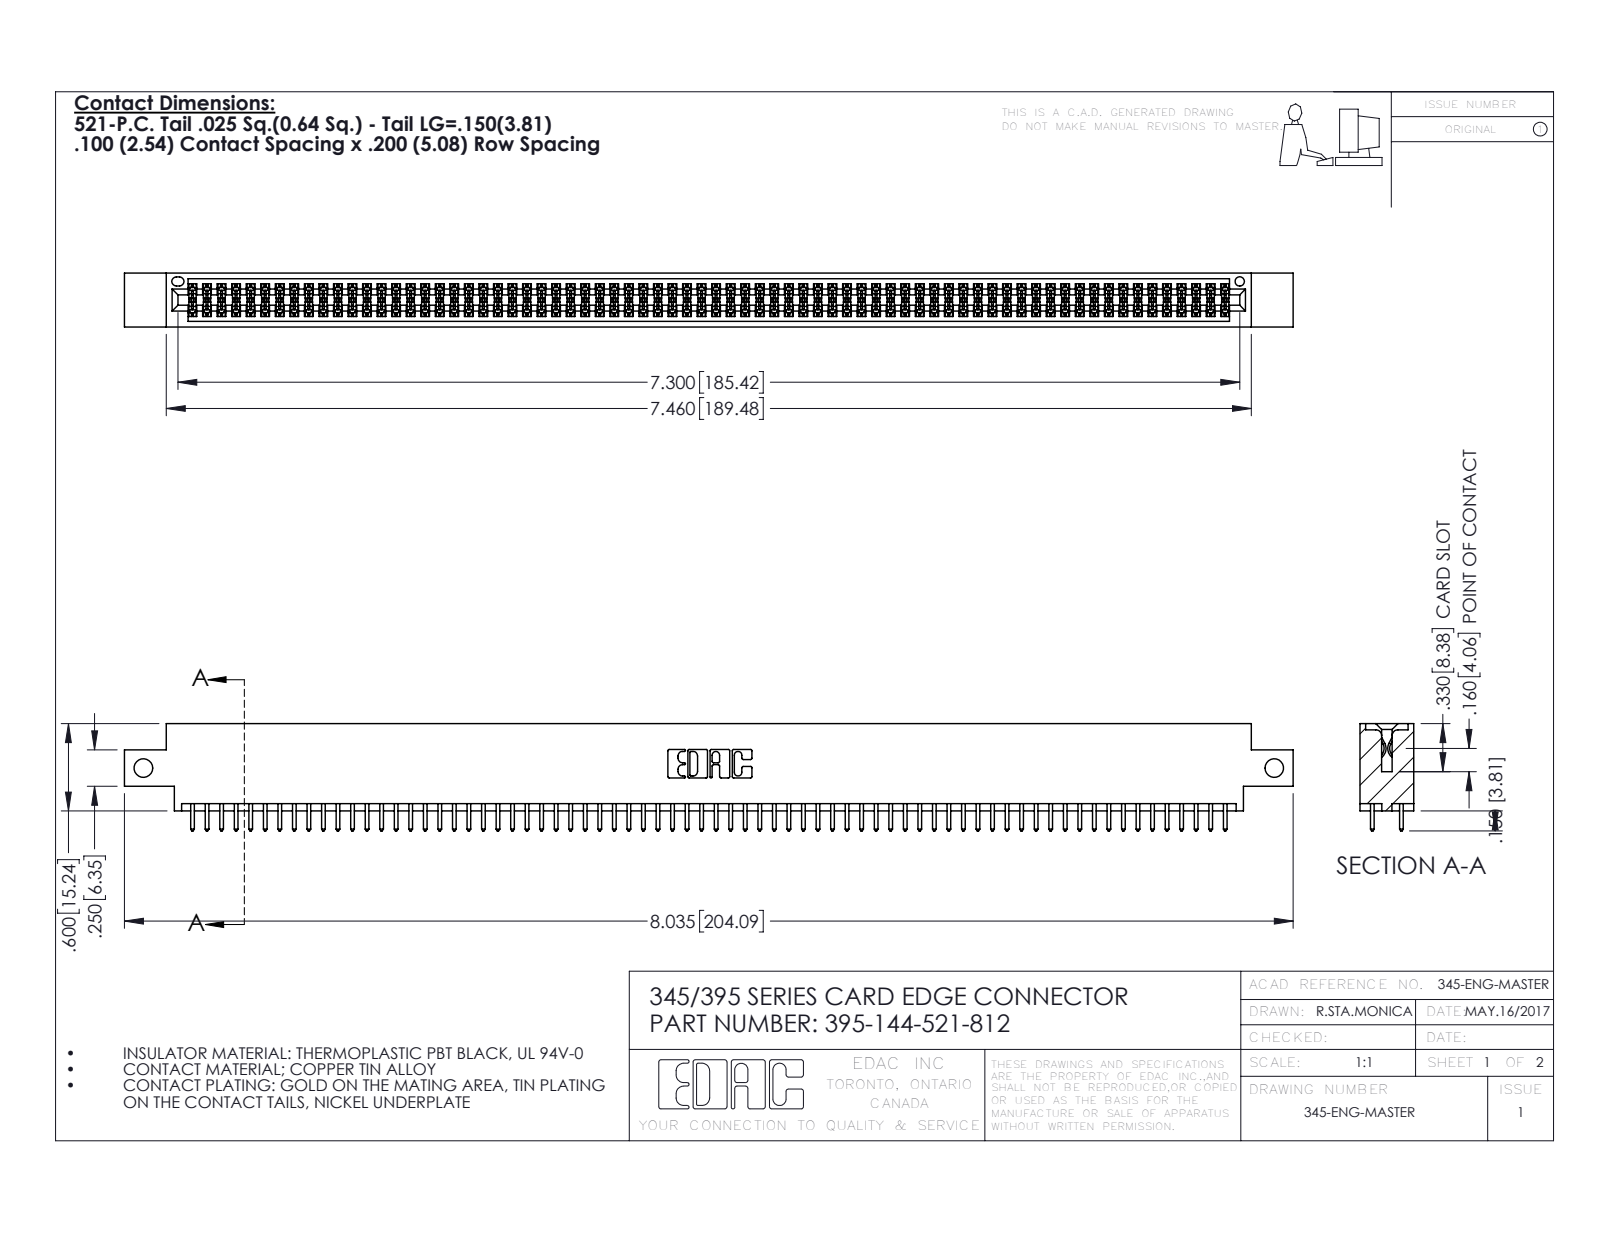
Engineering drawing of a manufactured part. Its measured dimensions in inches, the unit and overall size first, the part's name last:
Units: inches
Overall size (bounding box): 8.035 × 0.737 × 0.37
Round holes (diameter × count): ⌀0.128 ×2, ⌀0.064 ×1
Partial cylindrical surfaces — rounded edges, fillets, slot ends (radius × count): R0.006 ×216, R0.01 ×144, R0.01 ×22, R0.007 ×6, R0.031 ×6, R0.026 ×3, R0.014 ×2, R0.019 ×2
Main face-to-face distances: 0.072, 0.298, 0.2, 0.37, 0.098, 0.272, 0.025, 0.225, 0.175, 0.149
Hole centre spacings: 7.775
Volume: 1.211 in³ · Surface area: 45.79 in²
Bodies: 145 solids, 7330 faces (4836 planar, 2494 cylindrical, 0 other)
Part name (STEP PRODUCT): 345-292-001_345-293-121; 345 Part_0.170 Offset - Side Mount; 395-144-521-812
STEP written by: SolidWorks 2016 (CONFIG_CONTROL_DESIGN)
